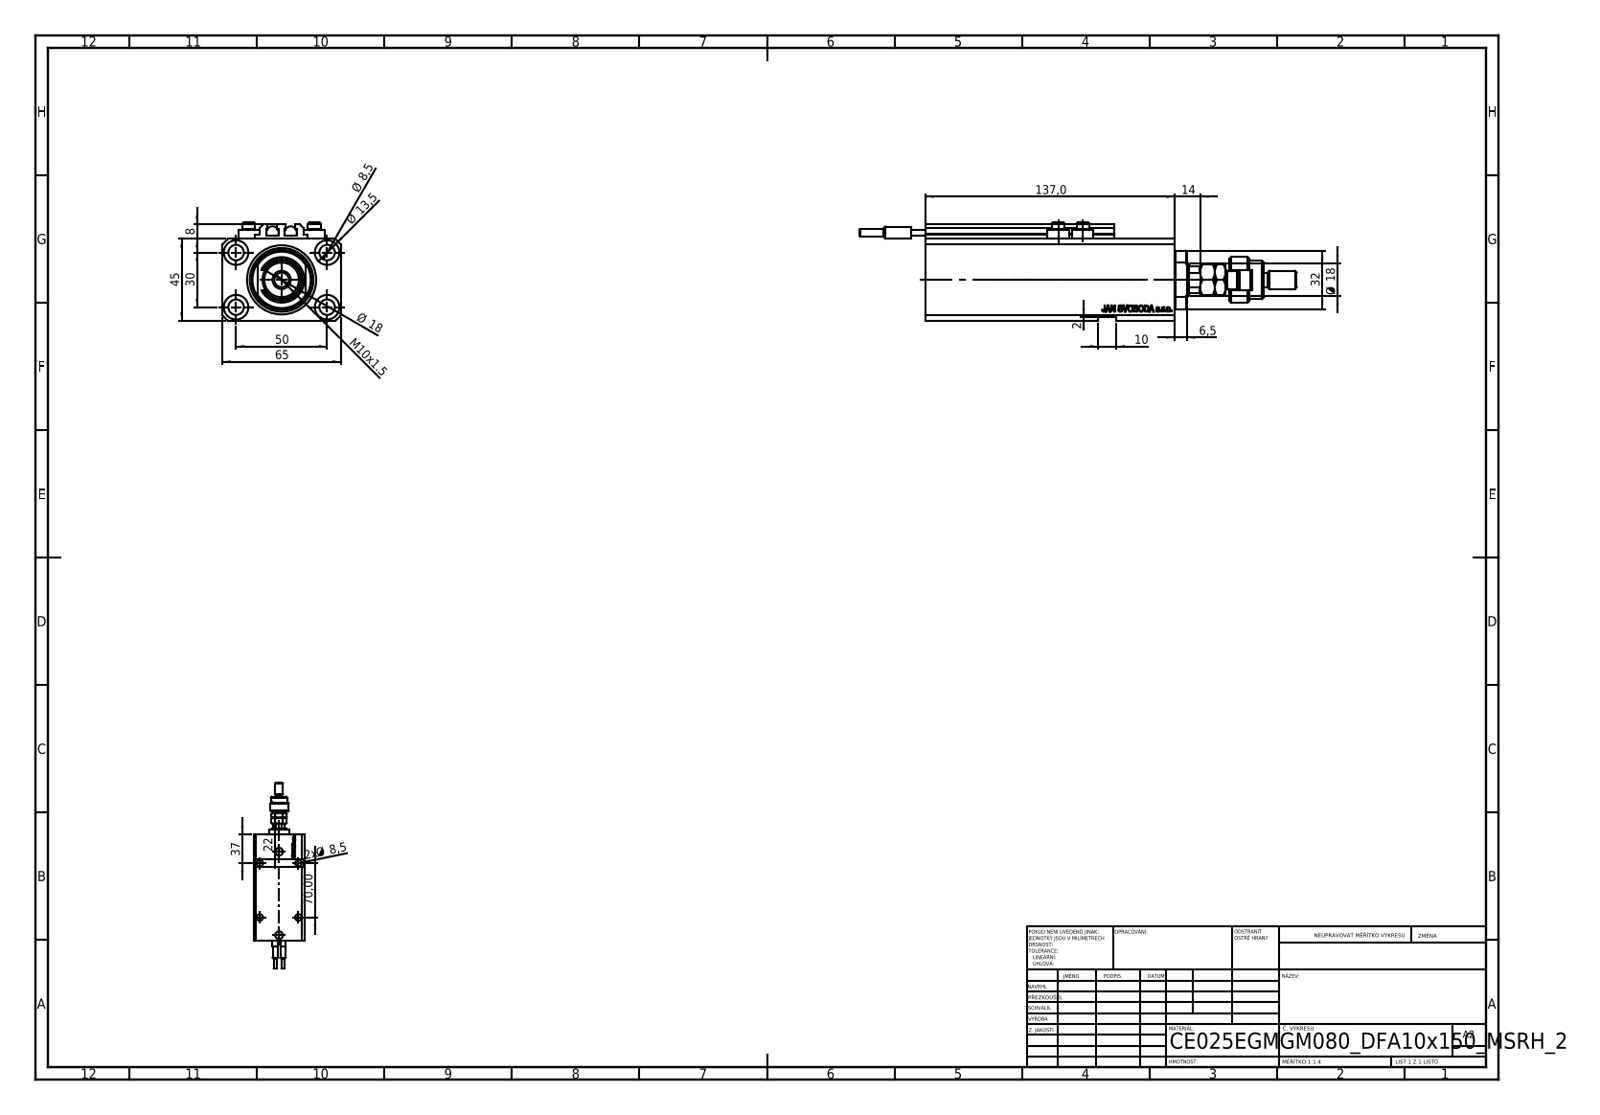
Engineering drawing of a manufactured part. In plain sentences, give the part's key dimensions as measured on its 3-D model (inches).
The part is named "V250CE_C_VCP; V250CE_E_Body; ALLEN BOLT V250CE; FEMALE_PART_FOR_DFA (+3 more)". Its 3-D file was written by "SolidWorks 2019 (CONFIG_CONTROL_DESIGN)". It is 12 solids with 1224 faces: 571 planar, 171 cylindrical and 482 other. Overall it measures 9.449 by 2.559 by 2.126 inches. Its volume is 22.33 cubic inches and its surface area 157.7 square inches. Round holes: 9 of diameter 0.335, 4 of diameter 0.049, 4 of diameter 0.157, 4 of diameter 0.531, 2 of diameter 0.394, 2 of diameter 0.518, 2 of diameter 0.787, 1 of diameter 0.709, 1 of diameter 1.496. Round bosses or shafts: 4 of diameter 0.457, 4 of diameter 0.276, 2 of diameter 0.268, 2 of diameter 0.256, 2 of diameter 0.157, 1 of diameter 0.984, 1 of diameter 0.827, 1 of diameter 0.63. Partial cylindrical surfaces (rounded edges, fillets, slot ends): 10 of radius 0.008, 1 of radius 0.217, 1 of radius 0.335, 1 of radius 0.344, 1 of radius 0.63. The main face-to-face distances are 1.772, 2.559, 0.551, 0.079, 1.85, 0.118, 0.098, 4.843, 0.394, 5.394. The hole center spacings are 1.148, 1.969, 0.535, 0.595, 1.098, 1.181, 1.323, 1.324.
